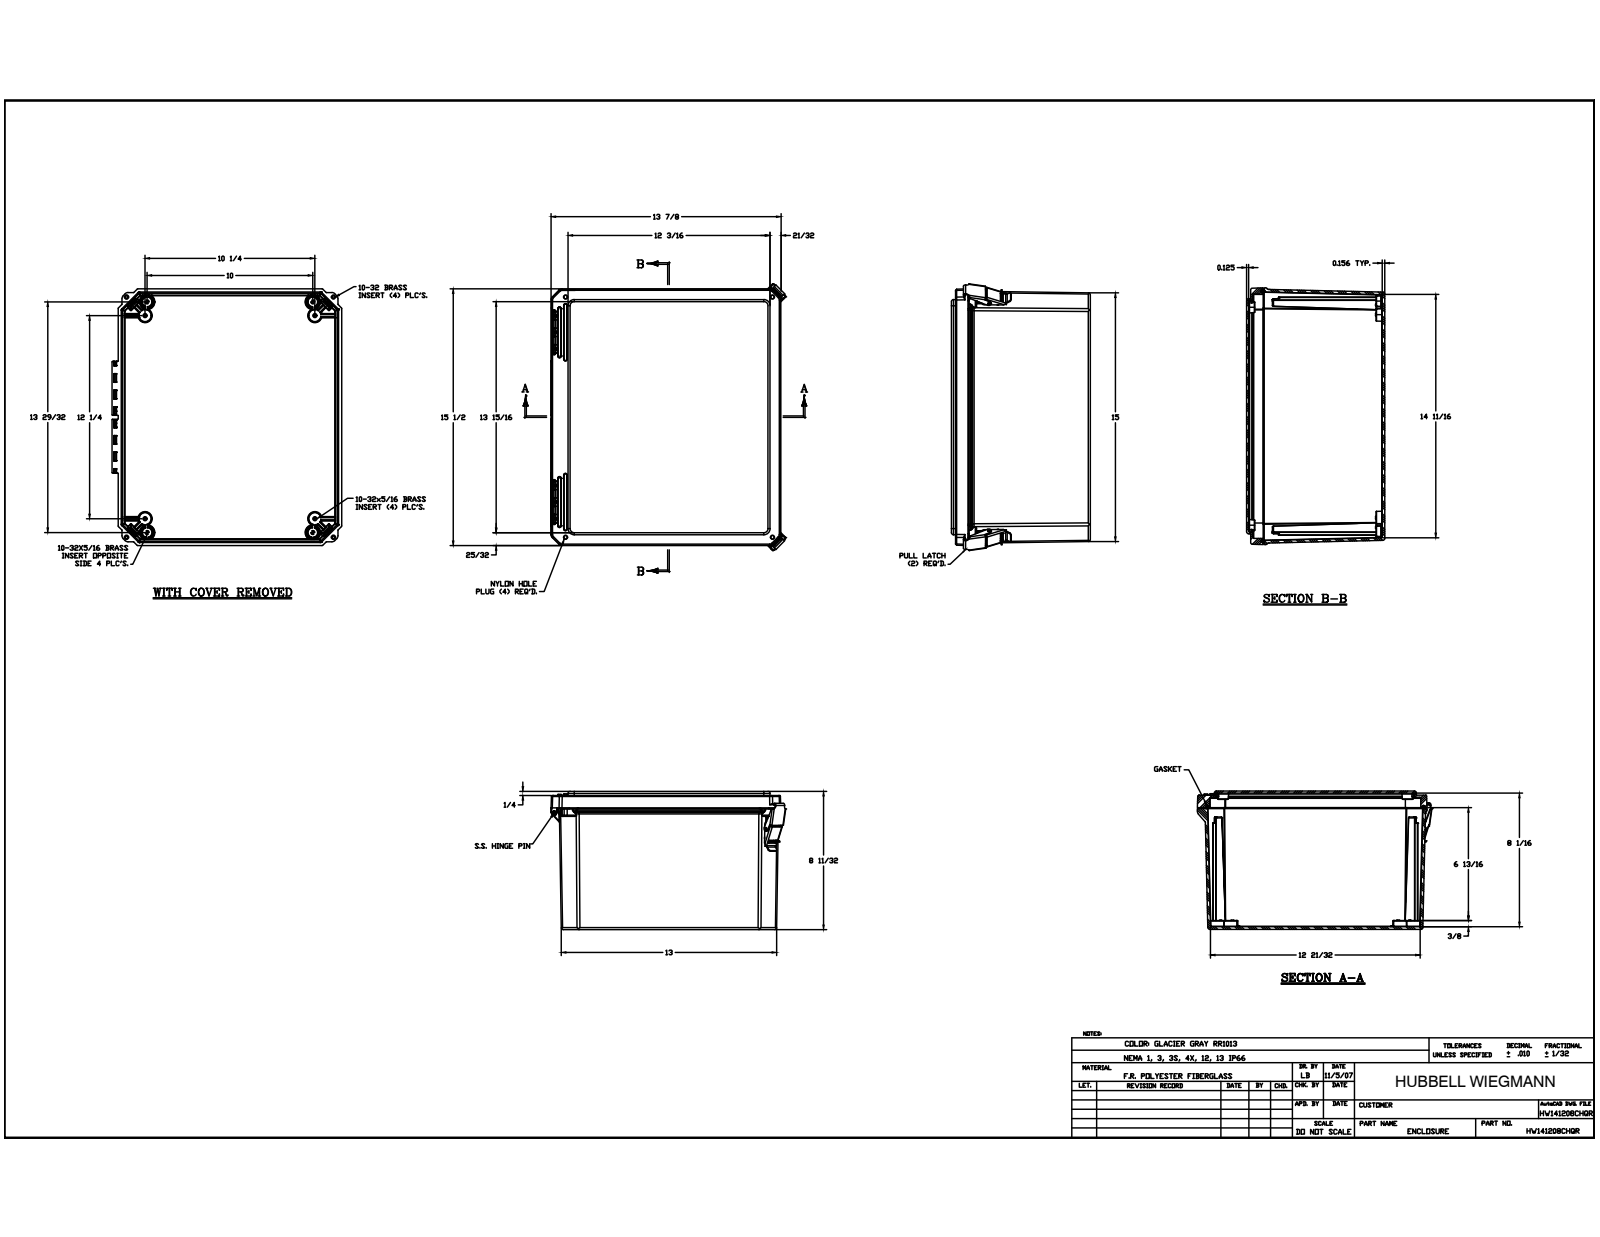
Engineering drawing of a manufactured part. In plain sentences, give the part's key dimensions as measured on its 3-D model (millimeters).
The part is named "DS141208BOX; BRASS INSERT-(; BRASS INSERT-(_1; BRASS INSERT-(_2 (+6 more)". Its 3-D file was written by "Autodesk Inventor 2014 (AUTOMOTIVE_DESIGN)". It is 35 solids with 2608 faces: 906 planar, 1046 cylindrical and 656 other. Overall it measures 411.48 by 361.26 by 211.87 millimeters. Its volume is 2 387 000 cubic millimeters and its surface area 1 198 000 square millimeters. Round holes: 16 of diameter 3.96, 8 of diameter 3.43, 8 of diameter 3.86, 4 of diameter 3.81, 4 of diameter 6.4, 4 of diameter 6.43, 2 of diameter 3.43, 2 of diameter 5.56, 2 of diameter 5.77, 2 of diameter 7.94, 2 of diameter 9.52, 1 of diameter 3.48. Round bosses or shafts: 16 of diameter 6.25, 4 of diameter 5.3, 2 of diameter 11.05, 2 of diameter 7.62, 1 of diameter 3.43. Partial cylindrical surfaces (rounded edges, fillets, slot ends): 210 of radius 0.25, 111 of radius 0.51, 88 of radius 0.13, 65 of radius 0.76, 35 of radius 1.52, 28 of radius 1.59, 26 of radius 2.29, 24 of radius 0.76. The main face-to-face distances are 3.96, 3.17, 207.91, 4.07, 211.87, 4.03, 208.7, 204.74, 6.35, 3.18. The hole center spacings are 6.36, 40.23, 290.19, 340.78, 445.77, 272, 322.78, 351.43.
